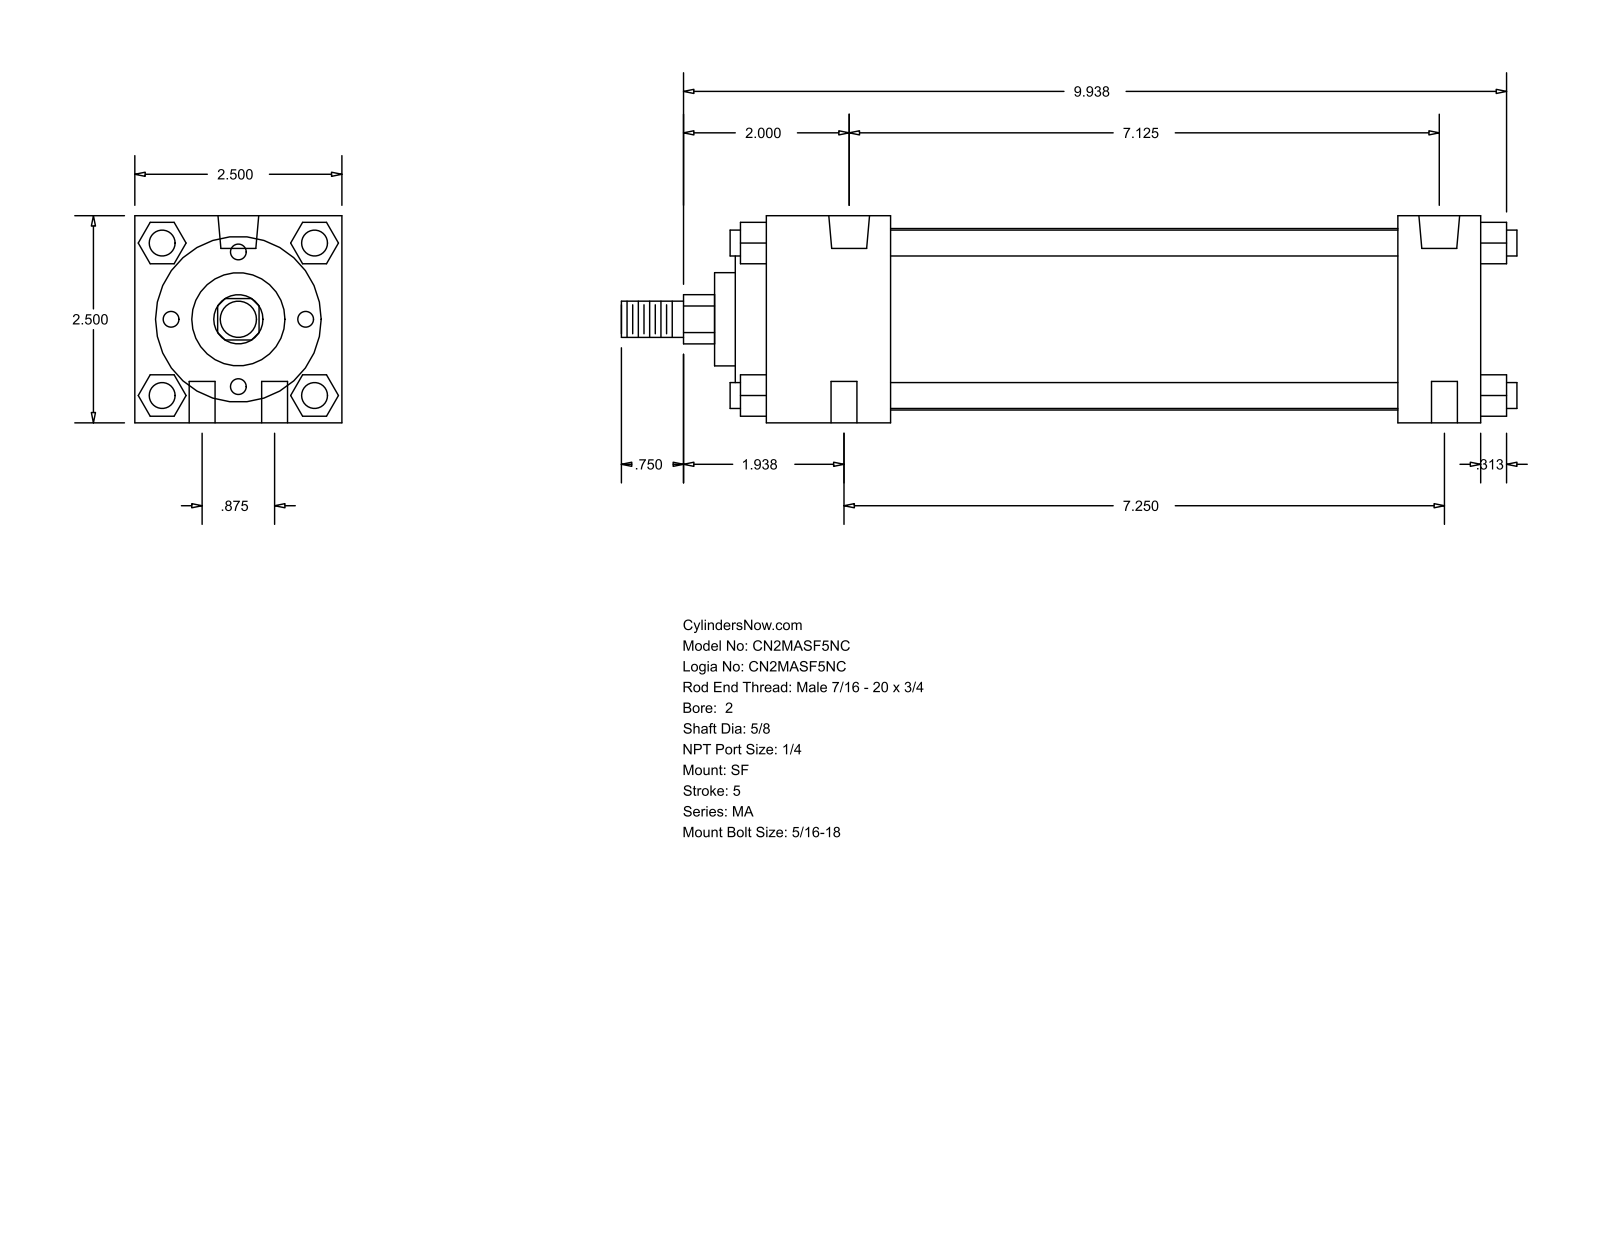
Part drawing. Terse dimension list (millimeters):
name: MA_SF__0200_0.625
written by: GSSL Pune (CONFIG_CONTROL_DESIGN)
unit: mm
bodies: 0 solids, 126 faces (95 planar, 31 cylindrical, 0 other)
size: 274.64 × 63.5 × 63.5
holes: 6× ⌀7.94, 2× ⌀12.49
bosses: 4× ⌀7.94, 1× ⌀55.63, 1× ⌀50.8, 1× ⌀28.57, 1× ⌀15.88, 1× ⌀11.11
rounds: 1× R7.54
face distances: 63.5, 25.4, 12.7, 38.1, 219.07, 193.67, 155.57, 180.97, 9.52, 47.62
hole spacings: 11.22, 22.22, 180.98, 182.9, 182.91, 184.15, 185.49
